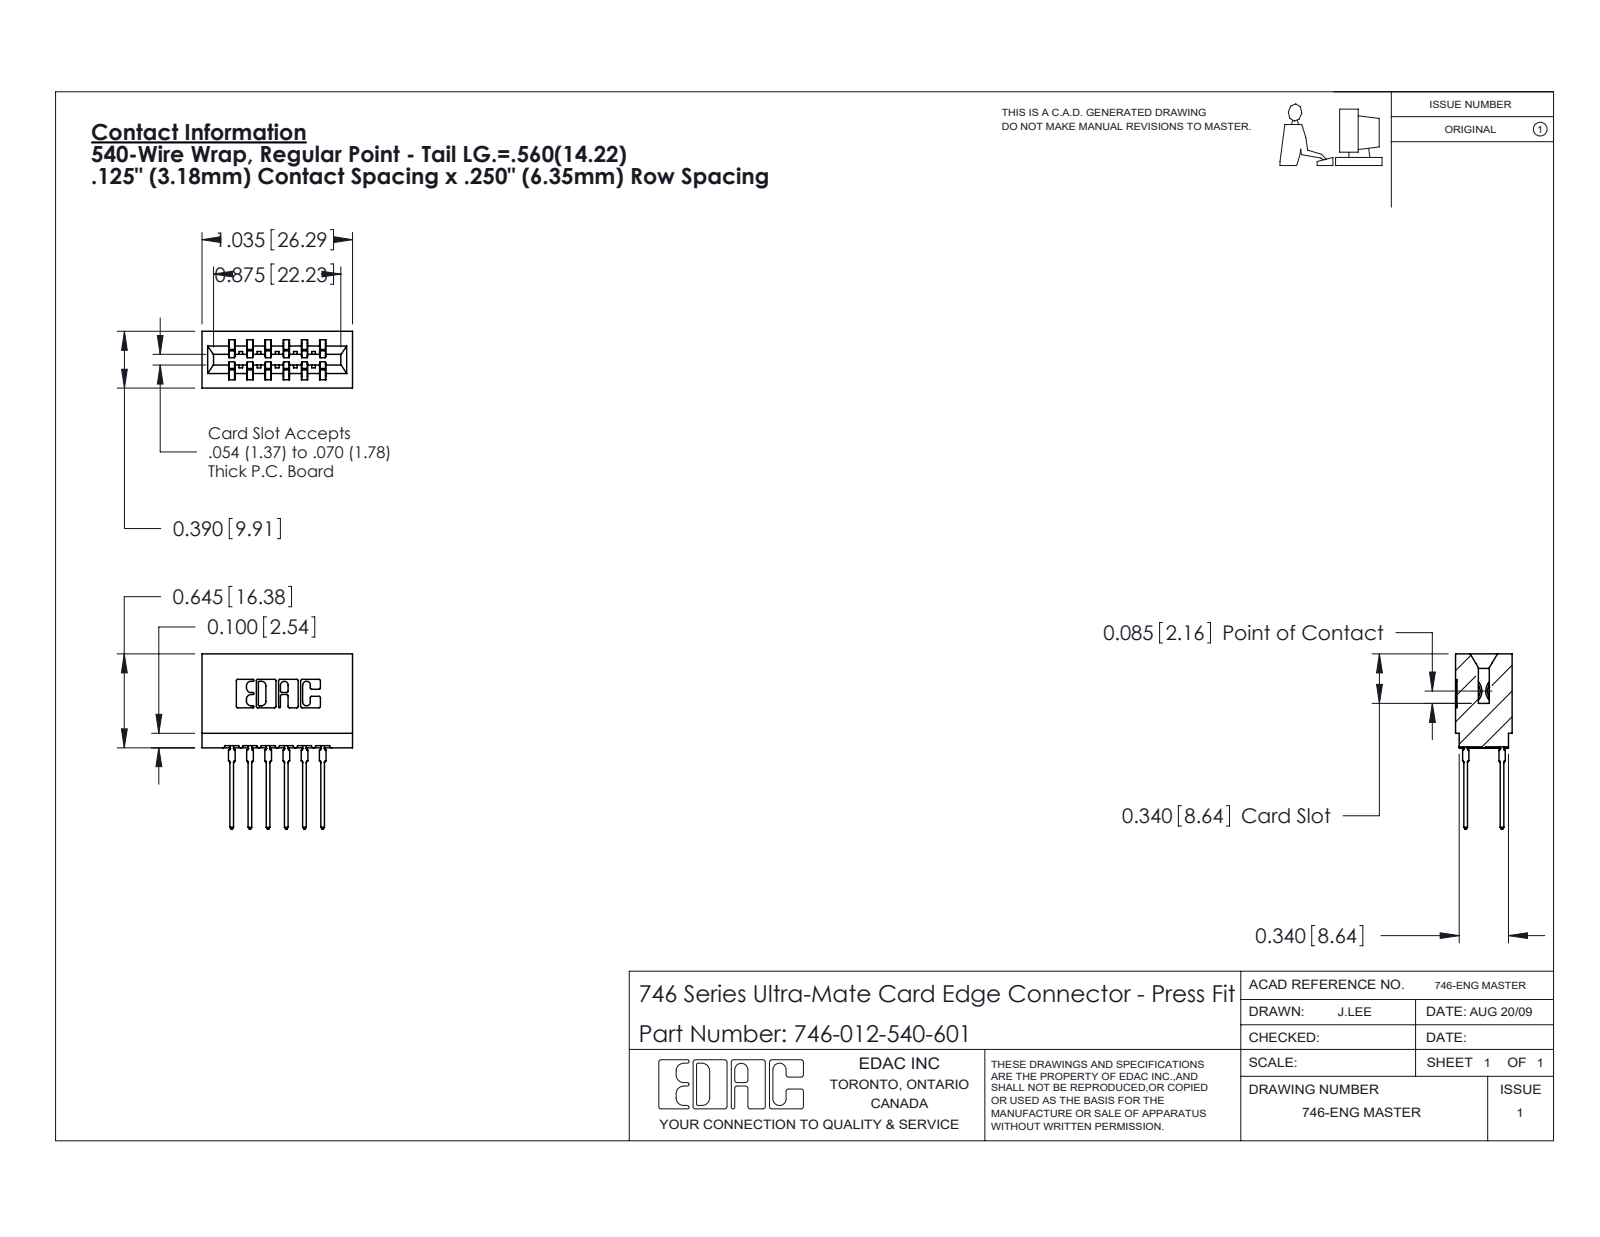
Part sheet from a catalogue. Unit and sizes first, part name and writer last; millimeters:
Units: millimetres
Overall size (bounding box): 30.6 × 26.3 × 9.9
Partial cylindrical surfaces — rounded edges, fillets, slot ends (radius × count): R0.5 ×24, R0.3 ×22, R0.1 ×8, R0.3 ×8, R0.4 ×7, R0.2 ×6, R0.8 ×6, R0.7 ×3
Main face-to-face distances: 6.4, 1.4, 3.2, 1.1, 8.5, 3.2, 9.5, 12.7, 2.1, 9.9
Volume: 3 260 mm³ · Surface area: 4 299 mm²
Bodies: 13 solids, 1171 faces (607 planar, 252 cylindrical, 312 other)
Part name (STEP PRODUCT): 746 Part_.340 Slot Depth - 01; 746-292-001_540; 746-012-540-601
STEP written by: SolidWorks 2020 (CONFIG_CONTROL_DESIGN)
